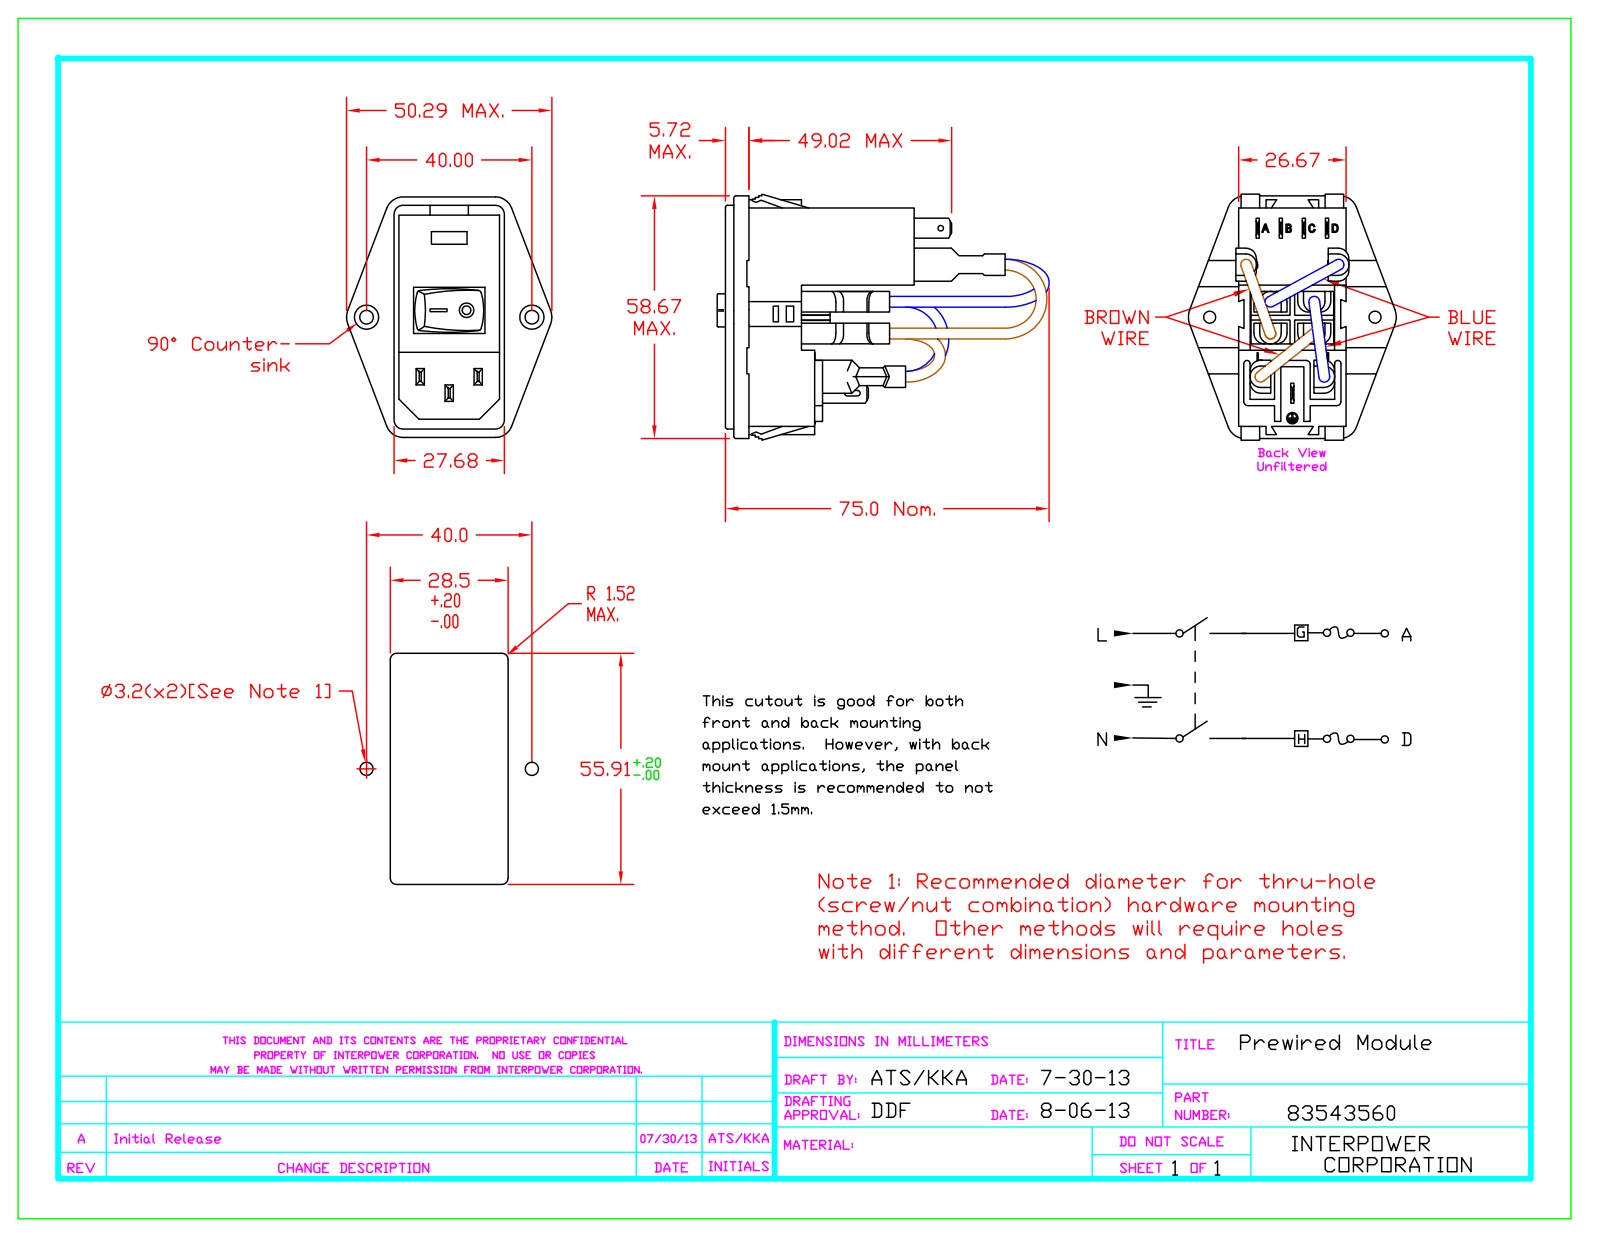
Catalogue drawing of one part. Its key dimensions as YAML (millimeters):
part_name: "Part18^83543560; Part19^83543560; 83543560; 83543060 (+3 more)"
step_written_by: "SolidWorks 2013 (AUTOMOTIVE_DESIGN)"
units: millimeters
bodies: {solids: 13, faces: 860, planar: 589, cylindrical: 205, other: 66}
overall_size: [80.3, 59.5, 50.3]
volume: 43150
surface_area: 23010
round_holes:
  - {diameter: 2.6, count: 8}
  - {diameter: 1.3, count: 5}
  - {diameter: 2.9, count: 2}
  - {diameter: 2.3, count: 1}
  - {diameter: 3.5, count: 1}
round_bosses_or_shafts:
  - {diameter: 2.9, count: 1}
  - {diameter: 2.7, count: 1}
partial_cylinders:
  - {radius: 2.6, count: 72}
  - {radius: 1, count: 19}
  - {radius: 0.5, count: 10}
  - {radius: 0.3, count: 5}
  - {radius: 2.2, count: 4}
  - {radius: 4.2, count: 4}
  - {radius: 0.7, count: 2}
  - {radius: 0.8, count: 2}
face_to_face_distances: [26, 18.6, 3.7, 5.7, 2, 18.2, 40, 43.6, 45.7, 0.5]
hole_center_spacings: [10.6, 7.7, 10.7, 10.7, 12.6, 13.1, 15.2, 15.2]
